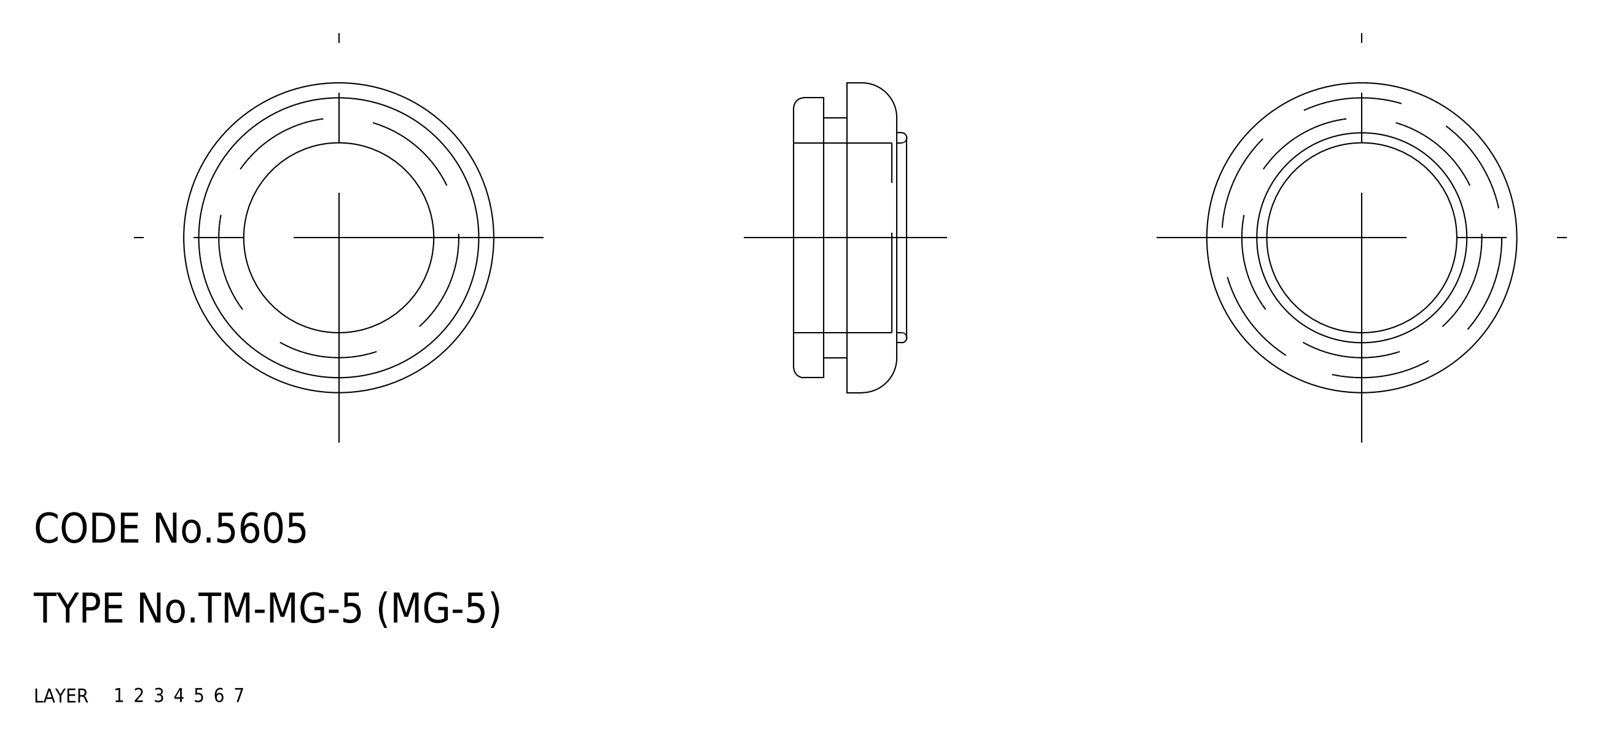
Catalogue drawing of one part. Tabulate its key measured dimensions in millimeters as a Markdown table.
| quantity | value |
| --- | --- |
| part name | grommet |
| STEP written by | CADfix (AUTOMOTIVE_DESIGN) |
| units | millimeters |
| bodies | 1 solid, 24 faces (0 planar, 0 cylindrical, 24 other) |
| overall size | 31 × 31 × 11.3 |
| volume | 3 689 mm³ |
| surface area | 3 256 mm² |
